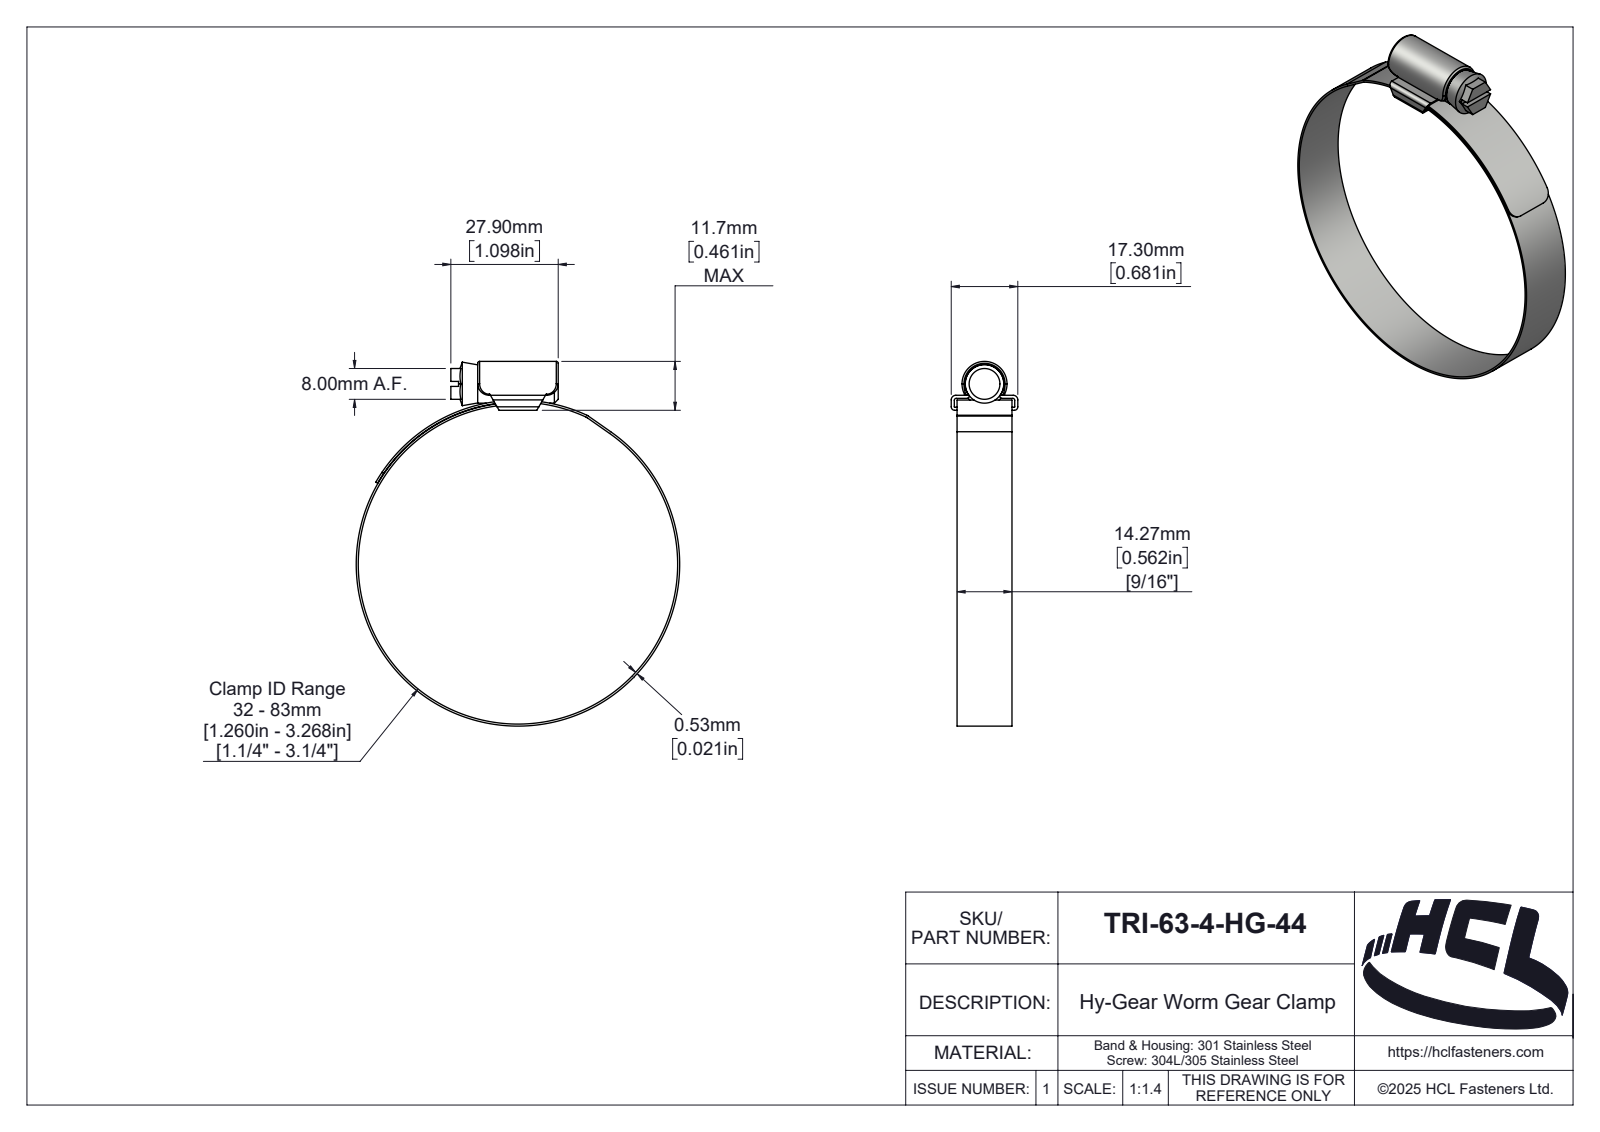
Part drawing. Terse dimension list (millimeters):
name: TRI-50-0-HG-44
written by: SolidWorks 2025 (AUTOMOTIVE_DESIGN)
unit: mm
bodies: 3 solids, 189 faces (39 planar, 89 cylindrical, 61 other)
size: 94.73 × 84.06 × 17.3
volume: 5 113 mm³; area: 11 891 mm²
holes: 1× ⌀83
bosses: 1× ⌀84.06, 1× ⌀10
rounds: 6× R0.5, 4× R3, 2× R0.1, 2× R0.9, 2× R1.2, 1× R0.46, 1× R1.89, 1× R2
face distances: 0.8, 3.1, 14.26, 0.53, 2.3, 3.9, 27.9, 1.52, 15.78, 16.5
